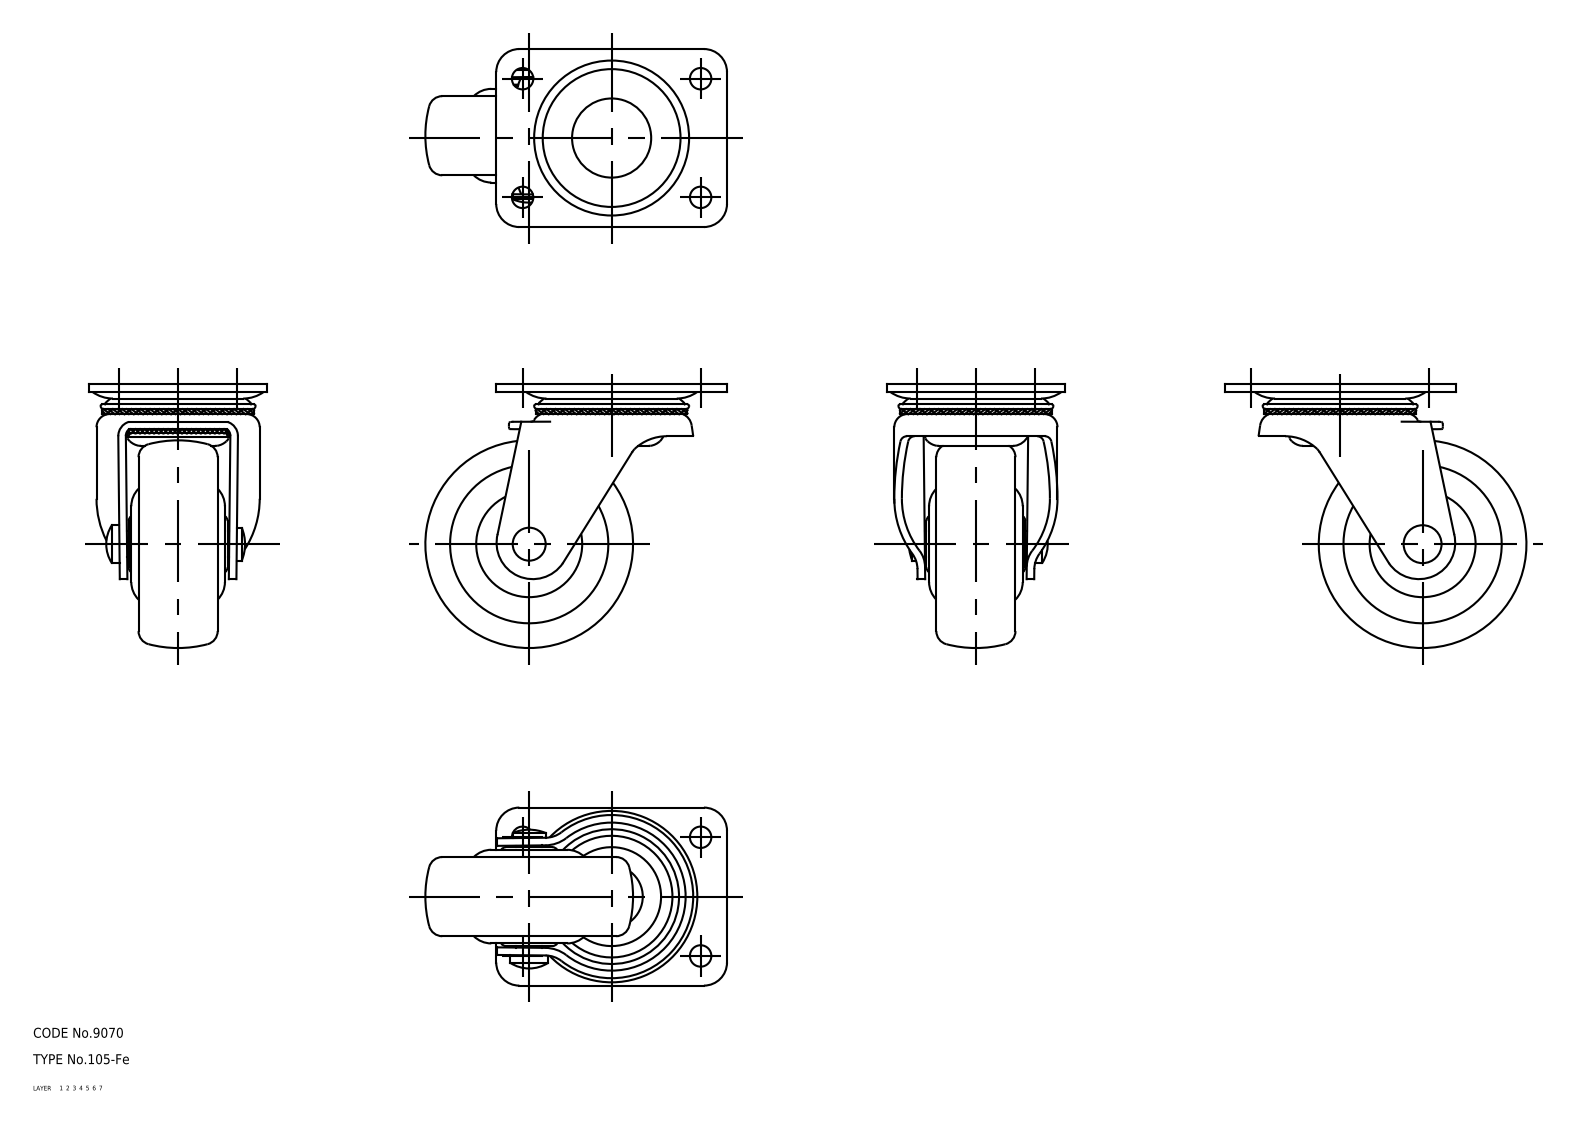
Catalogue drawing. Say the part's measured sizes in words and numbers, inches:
The part is named "wheel; mounting plate; main shaft; axle (+1 more)". Its 3-D file was written by "CADfix (AUTOMOTIVE_DESIGN)". It is 5 solids with 215 faces: 0 planar, 0 cylindrical and 215 other. Overall it measures 3.602 by 3.15 by 2.126 inches. Its volume is 6.648 cubic inches and its surface area 54.75 square inches.
